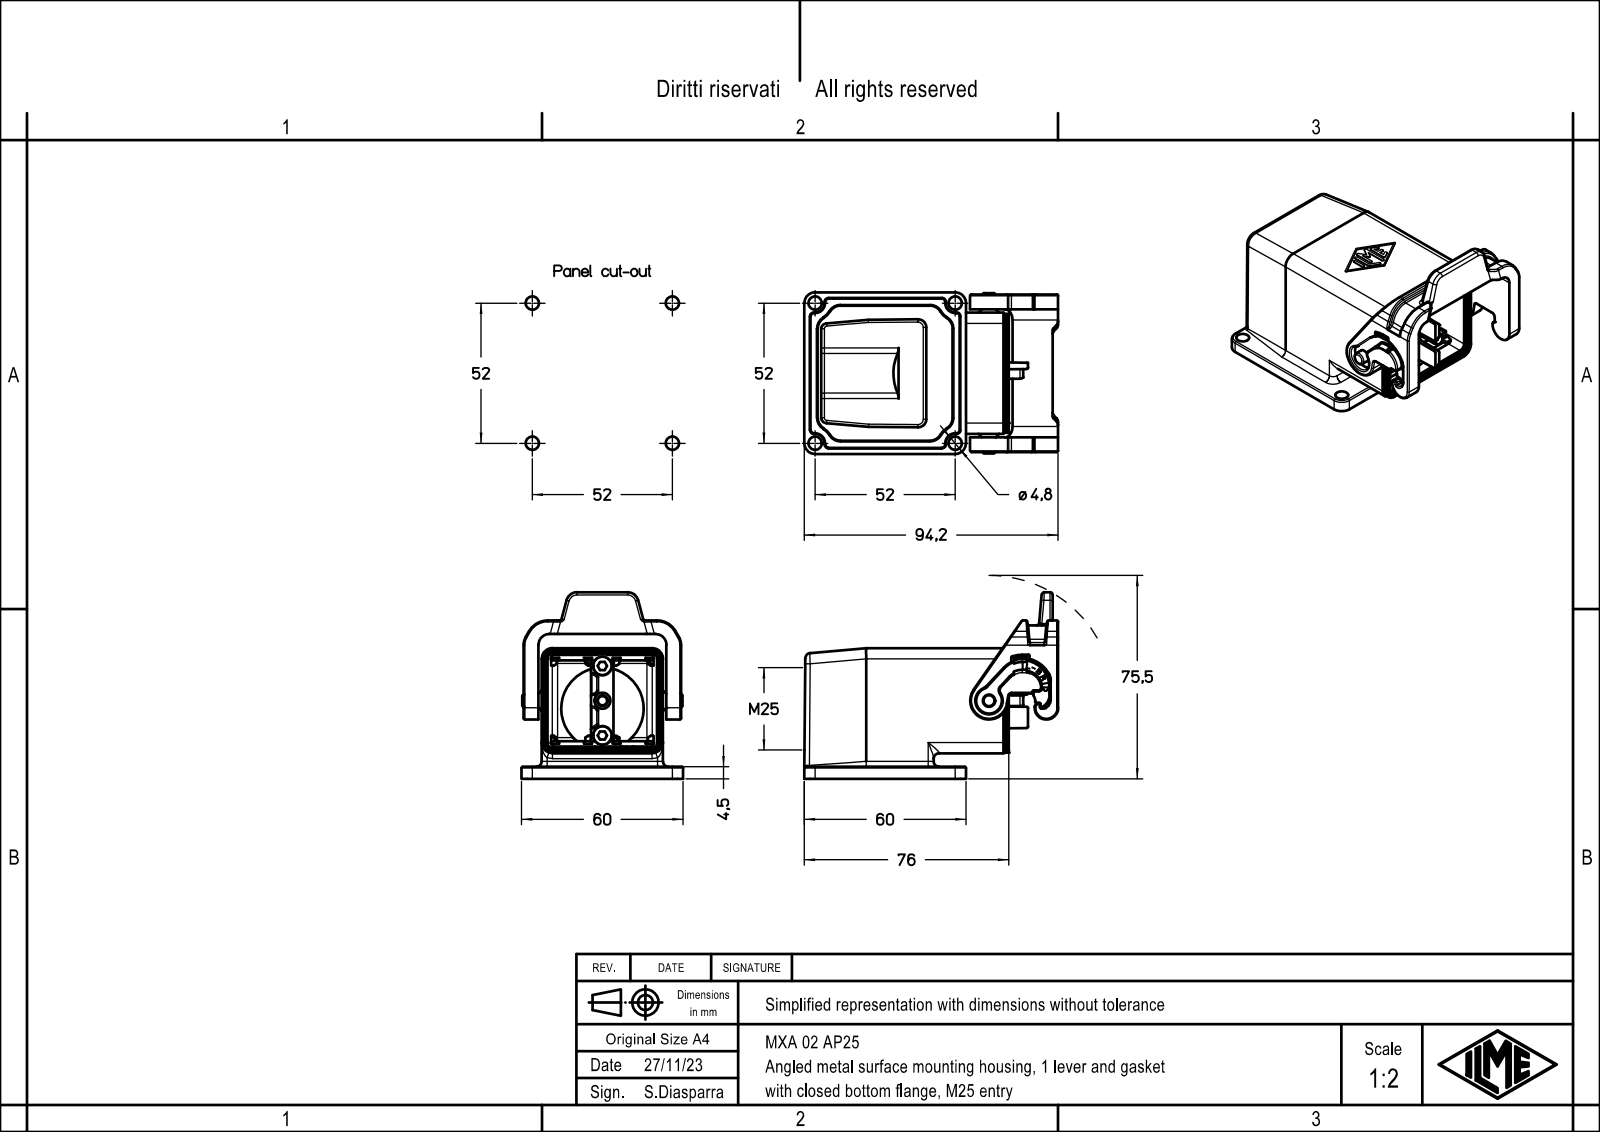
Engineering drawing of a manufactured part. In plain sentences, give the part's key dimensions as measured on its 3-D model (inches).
The part is named "MXA 02 AP25". Its 3-D file was written by "Creo Elements/Direct Modeling 20.1B 02-Apr-2019 (C) Parametric Technology GmbH (AUTOMOTIVE_DESIGN)". It is 1 solid with 1715 faces: 946 planar, 470 cylindrical and 299 other. Overall it measures 3.709 by 2.726 by 2.362 inches. Its volume is 3.954 cubic inches and its surface area 72.54 square inches. Round holes: 1 of diameter 0.929. Round bosses or shafts: 2 of diameter 0.276, 2 of diameter 0.157, 1 of diameter 0.236, 1 of diameter 0.142. Partial cylindrical surfaces (rounded edges, fillets, slot ends): 105 of radius 0.02, 45 of radius 0.004, 35 of radius 0.039, 29 of radius 0.079, 22 of radius 0.059, 16 of radius 0.012, 15 of radius 0.008, 14 of radius 0.157. The main face-to-face distances are 1.772, 0.217, 0.049, 1.909, 0.177, 1.821, 1.732, 0.079, 0.197, 0.098.
